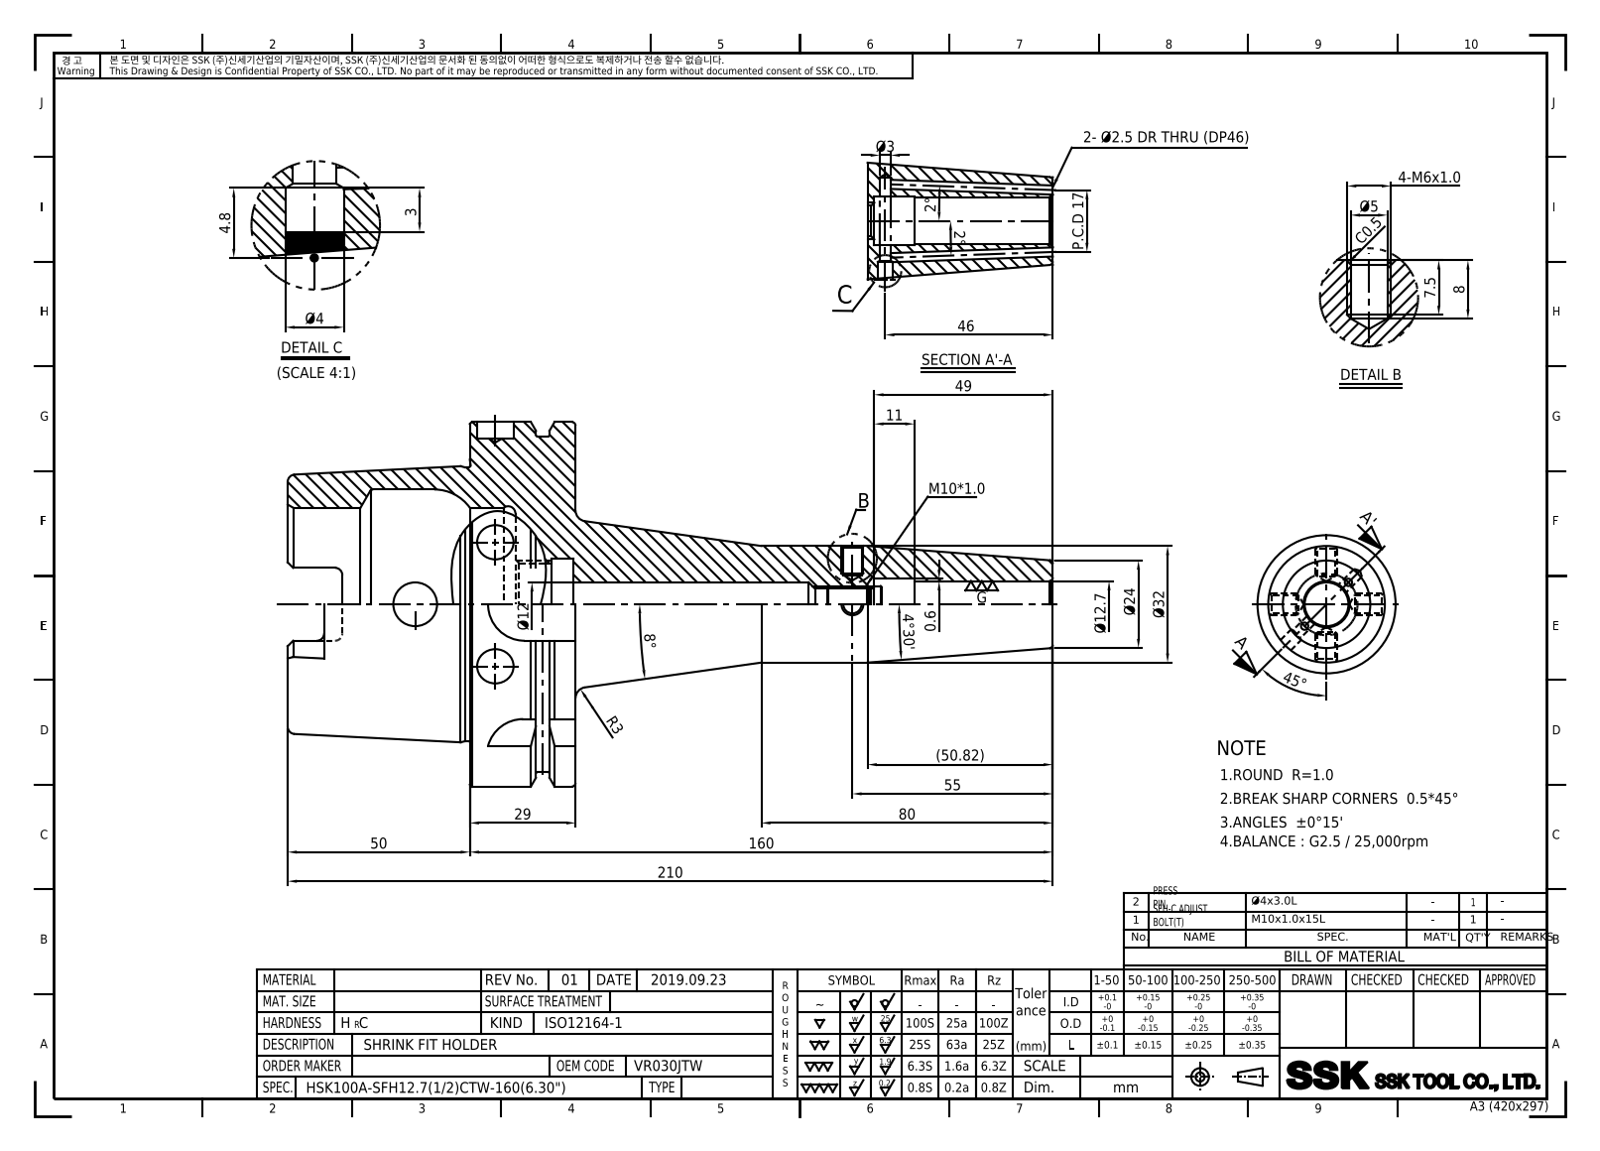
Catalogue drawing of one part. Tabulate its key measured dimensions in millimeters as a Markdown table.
| quantity | value |
| --- | --- |
| part name | LO-HSK100A-SFH12.7CTW-160 |
| STEP written by | Autodesk Inventor 2022 (AUTOMOTIVE_DESIGN) |
| units | millimeters |
| bodies | 1 solid, 120 faces (38 planar, 37 cylindrical, 45 other) |
| overall size | 210 × 100 × 100 |
| volume | 356 101 mm³ |
| surface area | 67 615 mm² |
| round holes (diameter × count) | 2.5 × 2, 12 × 2, 8.92 × 1, 10 × 1, 12.7 × 1, 13.9 × 1, 22.38 × 1, 25 × 1, 53 × 1, 63 × 1 |
| round bosses / shafts (diameter × count) | 100 × 1, 92 × 1, 75.41 × 1, 32 × 1 |
| partial cylindrical surfaces (radius × count) | 2 × 6, 4.88 × 4, 10 × 4 |
| main face-to-face distances | 29, 12.5, 16.5, 62.5, 50, 79, 88, 78.5, 28.5, 16 |
